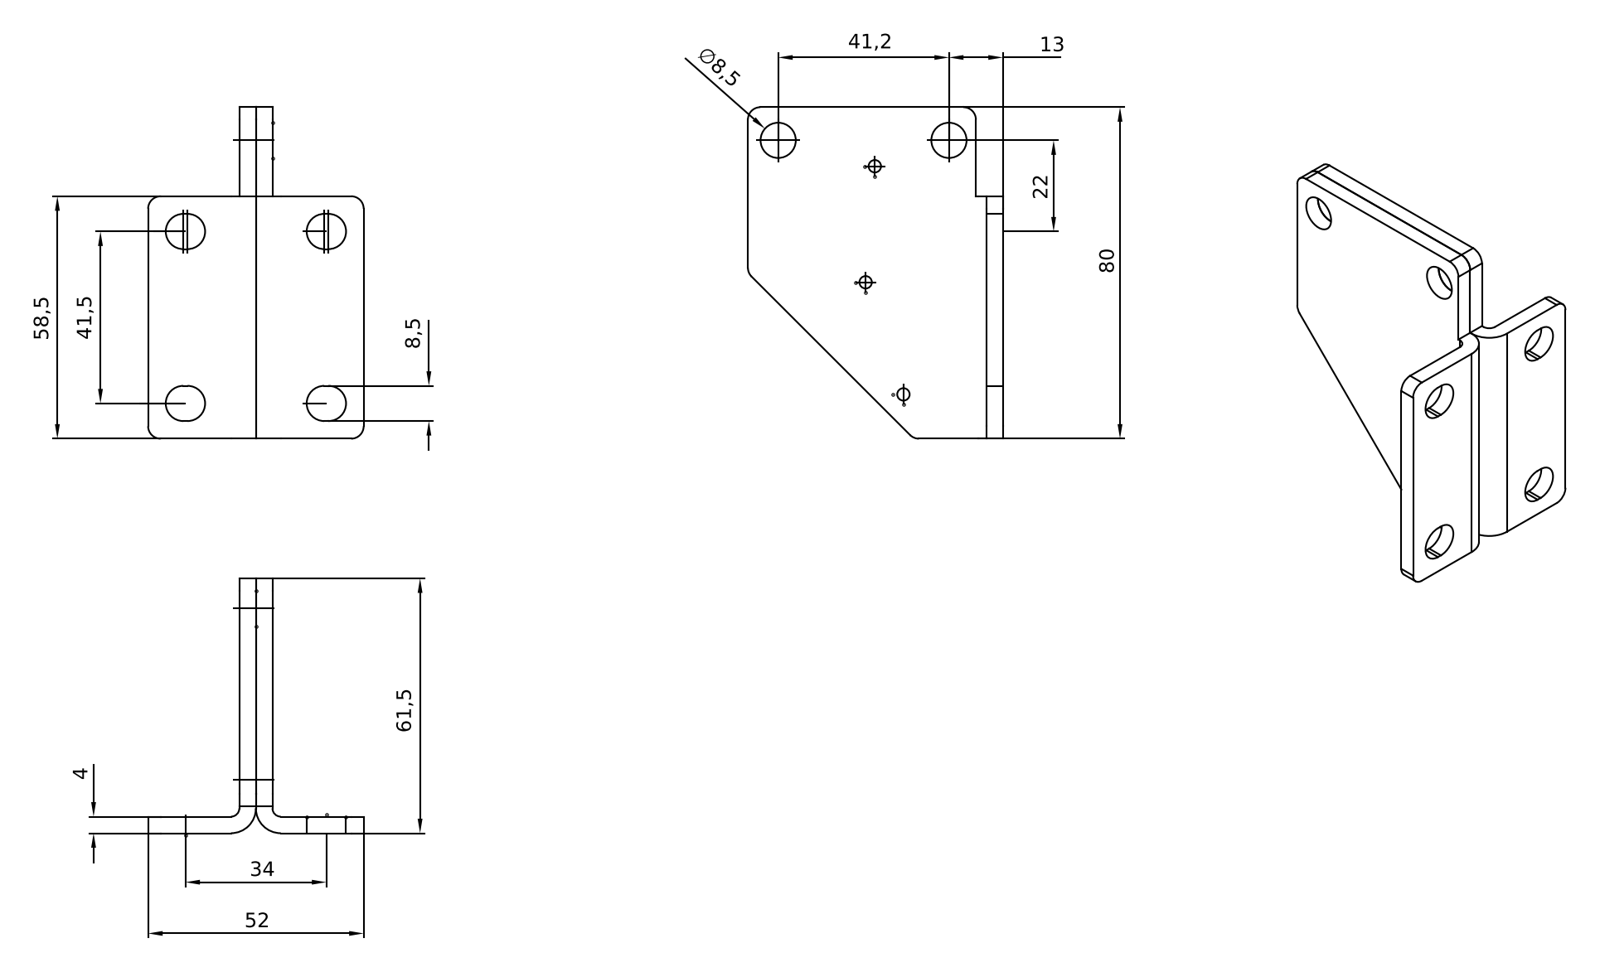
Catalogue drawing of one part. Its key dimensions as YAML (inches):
step_written_by: "Autodesk Inventor 8 (AUTOMOTIVE_DESIGN)"
units: inches
bodies: {solids: 1, faces: 58, planar: 14, cylindrical: 18, other: 26}
overall_size: [3.15, 2.421, 2.047]
volume: 2.399
surface_area: 24.61
partial_cylinders:
  - {radius: 0.118, count: 6}
  - {radius: 0.167, count: 4}
  - {radius: 0.079, count: 1}
  - {radius: 0.236, count: 1}
face_to_face_distances: [0.157, 3.15, 2.421, 2.264, 0.866, 2.303, 0.846, 0.256, 0.098, 2.165]
